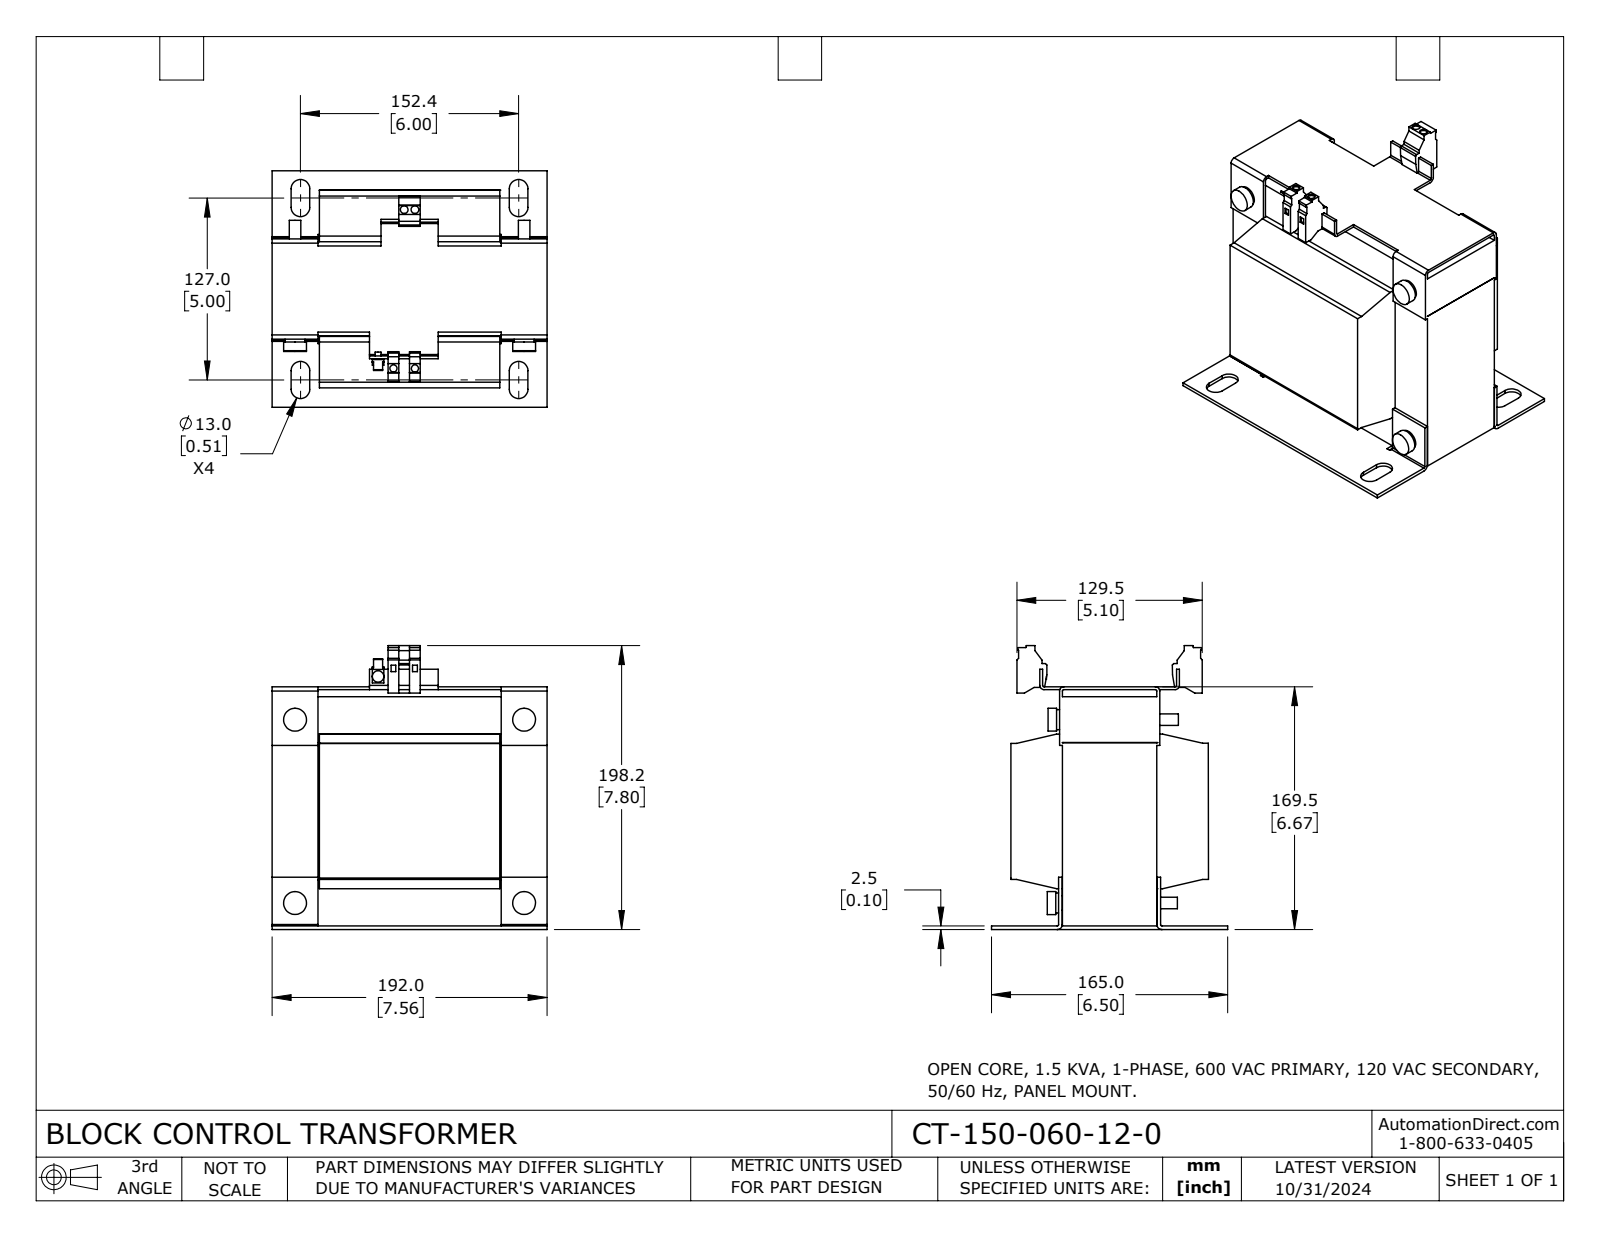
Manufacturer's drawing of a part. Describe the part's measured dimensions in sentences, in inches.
The part is named "CT-150-060-12-0". Its 3-D file was written by "SolidWorks 2023 (CONFIG_CONTROL_DESIGN)". It is 1 solid with 319 faces: 238 planar, 81 cylindrical and 0 other. Overall it measures 7.803 by 7.559 by 6.496 inches. Its volume is 187.3 cubic inches and its surface area 446.3 square inches. Round holes: 2 of diameter 0.197, 2 of diameter 0.213. Round bosses or shafts: 5 of diameter 0.315, 4 of diameter 0.63, 4 of diameter 0.551, 2 of diameter 0.394, 1 of diameter 0.157. Partial cylindrical surfaces (rounded edges, fillets, slot ends): 8 of radius 0.256, 6 of radius 0.039, 4 of radius 0.118, 2 of radius 0.138. The main face-to-face distances are 5.039, 1.26, 6.299, 0.098, 1.416, 4.015, 1.299, 6.26, 5.138, 0.079. The hole center spacings are 4.376, 0.295, 0.591, 4.366, 4.406.
